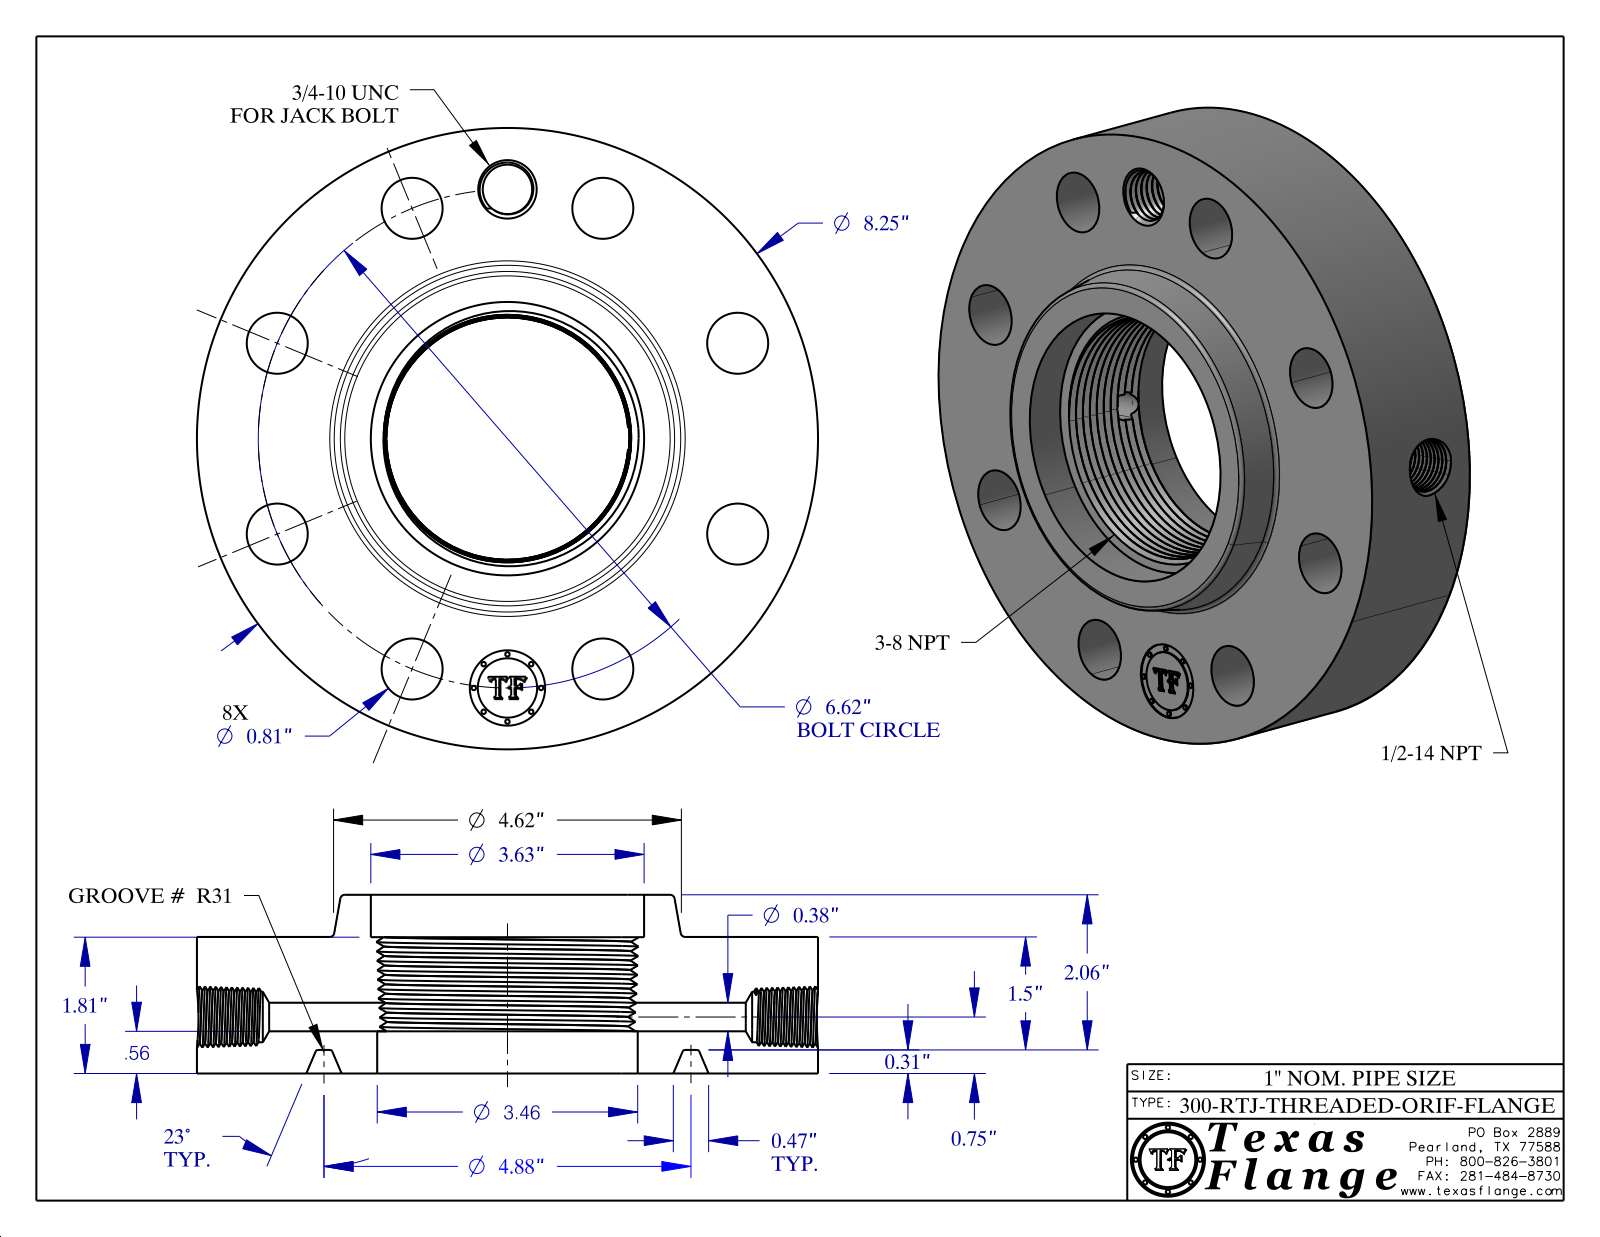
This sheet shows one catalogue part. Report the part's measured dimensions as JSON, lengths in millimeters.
{"part_name": "300-RTJ-THREADED", "step_written_by": "CATIA V5 STEP AP214 (AUTOMOTIVE_DESIGN)", "units": "millimeters", "bodies": {"solids": 1, "faces": 911, "planar": 372, "cylindrical": 96, "other": 443}, "overall_size": [209.6, 209.6, 60.3], "volume_mm3": 1194000, "surface_area_mm2": 147900, "round_holes": [[20.6, 8], [9.7, 1], [16.7, 1], [17.1, 1], [25.4, 1], [87.9, 1], [92.2, 1]], "round_bosses_or_shafts": [[1.5, 8], [209.6, 1], [20, 1]], "face_to_face_distances": [46.1, 14.2, 60.3, 8, 38.1, 52.3, 46, 38, 14.3, 6.3], "hole_center_spacings": [84.1, 118.9, 155.3, 168.1, 32.8, 64.3, 64.3, 93.4]}
